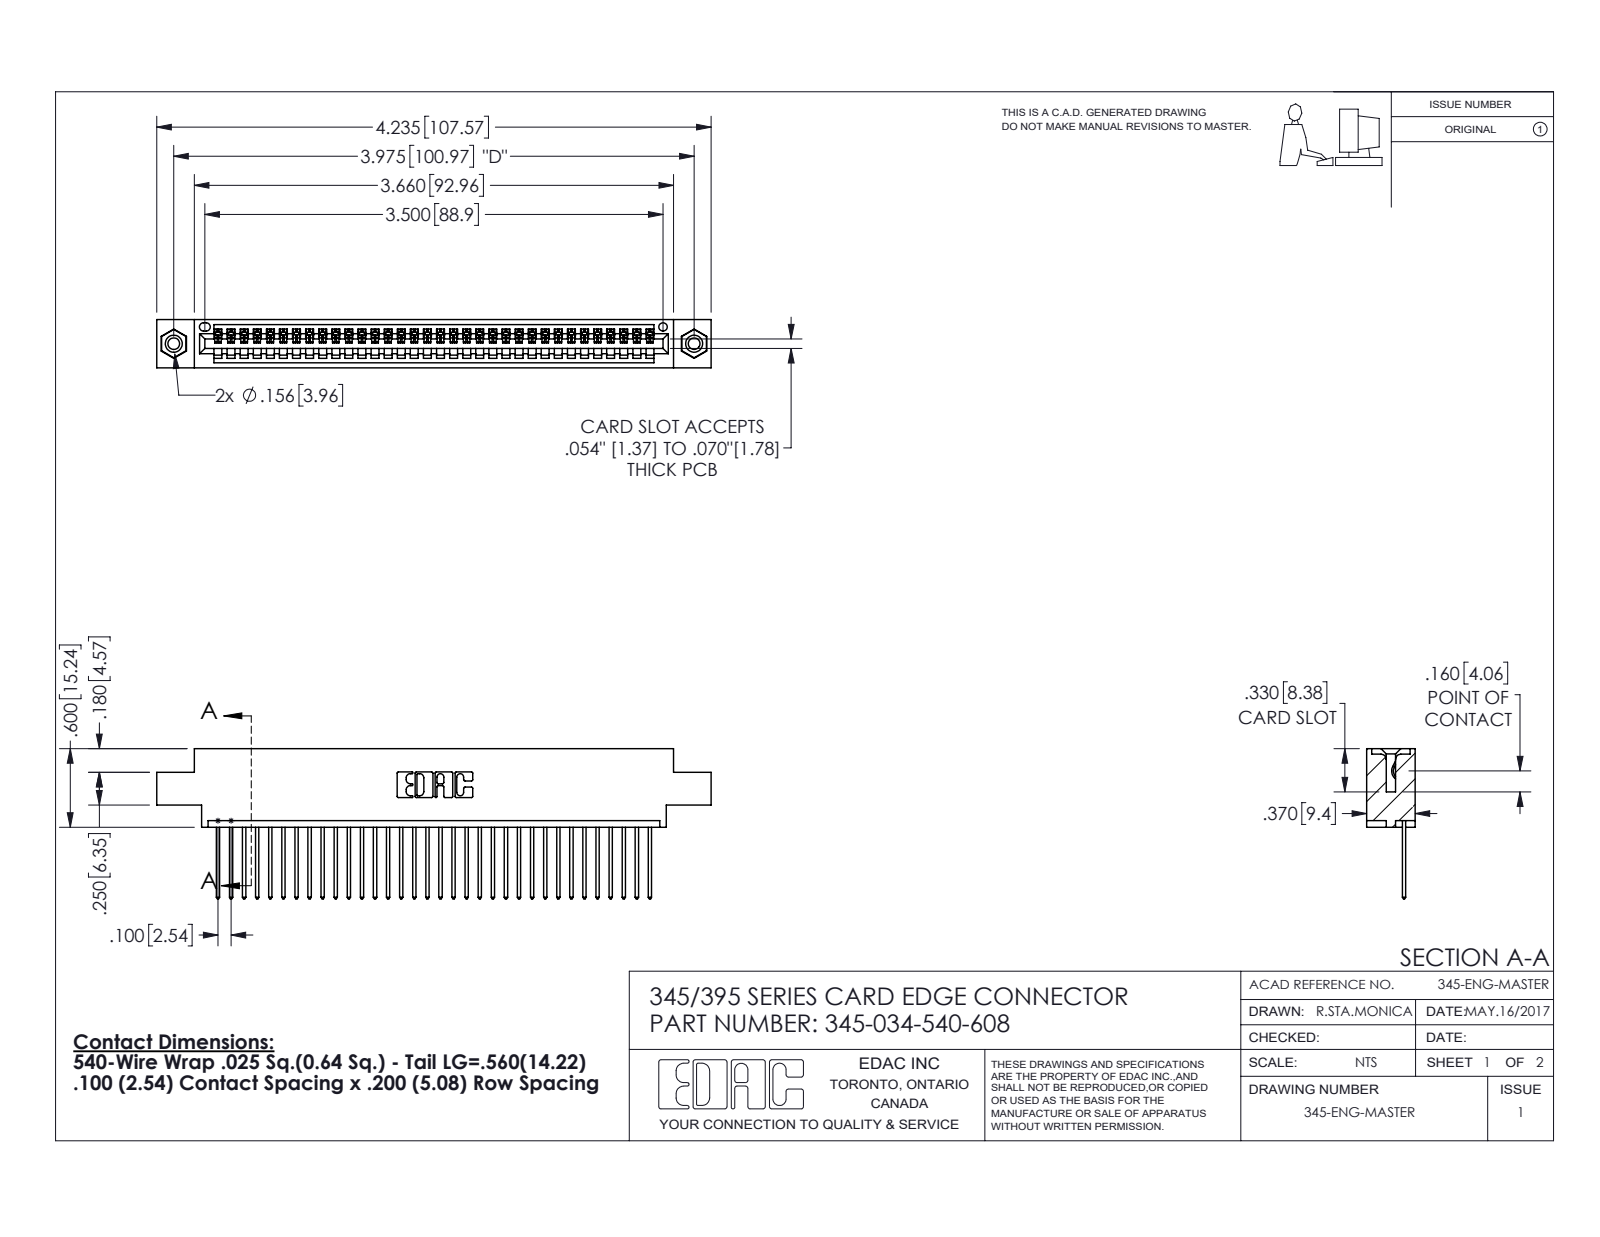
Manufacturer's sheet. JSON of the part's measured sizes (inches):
{"part_name": "345-034-540-608; 345-292-001_345-293-140; 345-250-001_345-250-003-102; 345 Part_0.170 Offset - 0.156 Dia-TI", "step_written_by": "SolidWorks 2016 (CONFIG_CONTROL_DESIGN)", "units": "inches", "bodies": {"solids": 37, "faces": 2162, "planar": 1476, "cylindrical": 670, "other": 16}, "overall_size": [4.235, 1.147, 0.37], "volume_in3": 0.615, "surface_area_in2": 21.33, "round_holes": [[0.089, 2], [0.125, 2], [0.156, 2], [0.064, 1]], "round_bosses_or_shafts": [[0.155, 2]], "partial_cylinders_radius": [[0.006, 68], [0.01, 68], [0.01, 22], [0.007, 6], [0.031, 6], [0.026, 3], [0.031, 2], [0.04, 2]], "face_to_face_distances": [0.072, 0.298, 0.37, 0.098, 0.272, 0.025, 0.2, 0.225, 0.175, 0.149], "hole_center_spacings": [0.27, 3.74, 3.975]}
